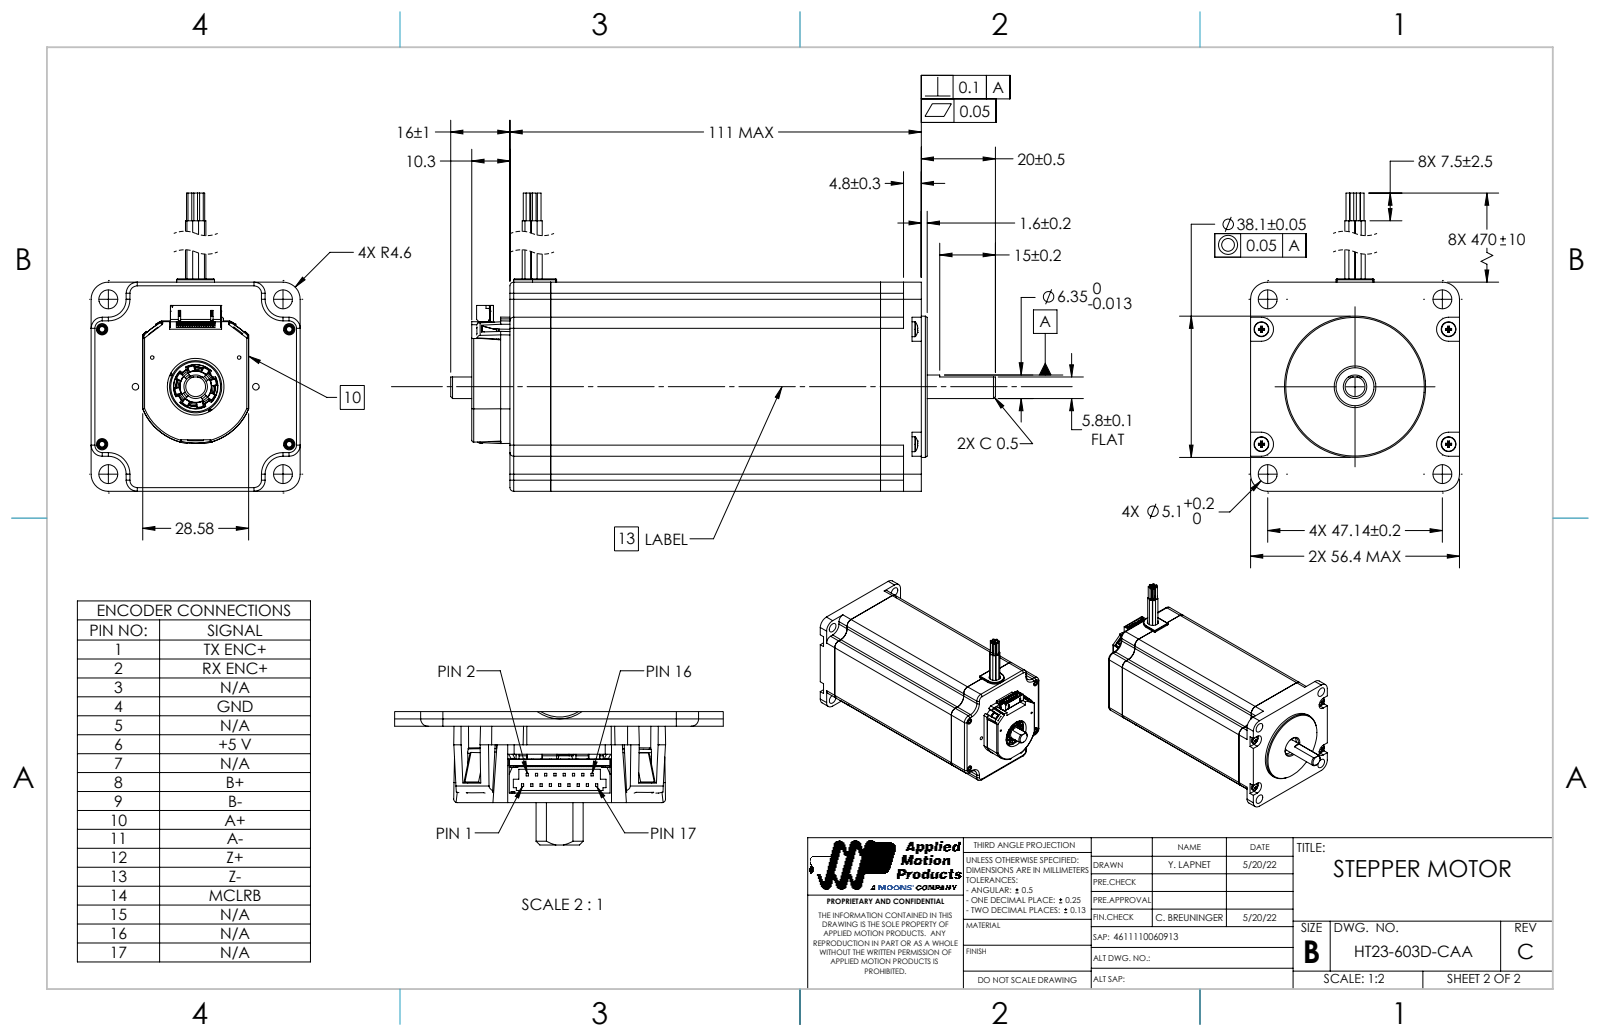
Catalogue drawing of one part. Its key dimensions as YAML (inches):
part_name: "HT23 Wire Grommet; HT23-603 Lead Wires (Break line); HT23D Rear Endbell; HT23-603D Shaft (+7 more)"
step_written_by: "SolidWorks 2017 (AUTOMOTIVE_DESIGN)"
units: inches
bodies: {solids: 34, faces: 6658, planar: 4811, cylindrical: 1580, other: 267}
overall_size: [5.787, 3.185, 2.22]
volume: 19.75
surface_area: 100.1
round_holes:
  - {diameter: 0.026, count: 168}
  - {diameter: 0.031, count: 6}
  - {diameter: 0.037, count: 4}
  - {diameter: 0.063, count: 4}
  - {diameter: 0.079, count: 4}
  - {diameter: 0.098, count: 4}
  - {diameter: 0.134, count: 4}
  - {diameter: 0.201, count: 4}
  - {diameter: 0.026, count: 2}
  - {diameter: 0.031, count: 2}
  - {diameter: 0.063, count: 2}
  - {diameter: 0.067, count: 2}
round_bosses_or_shafts:
  - {diameter: 0.063, count: 8}
  - {diameter: 0.039, count: 8}
  - {diameter: 0.157, count: 4}
  - {diameter: 0.079, count: 4}
  - {diameter: 0.059, count: 4}
  - {diameter: 0.051, count: 4}
  - {diameter: 0.094, count: 2}
  - {diameter: 1.5, count: 1}
partial_cylinders:
  - {radius: 0.38, count: 64}
  - {radius: 0.039, count: 39}
  - {radius: 0.498, count: 36}
  - {radius: 0.118, count: 8}
  - {radius: 0.02, count: 6}
  - {radius: 0.041, count: 6}
  - {radius: 0.079, count: 6}
  - {radius: 0.01, count: 5}
face_to_face_distances: [2.22, 3.504, 0.433, 3.937, 4.37, 0.372, 1.848, 0.175, 0.209, 0.642]
hole_center_spacings: [1.404, 1.167, 0.324, 0.354, 0.455, 0.5, 0.69, 0.706]
